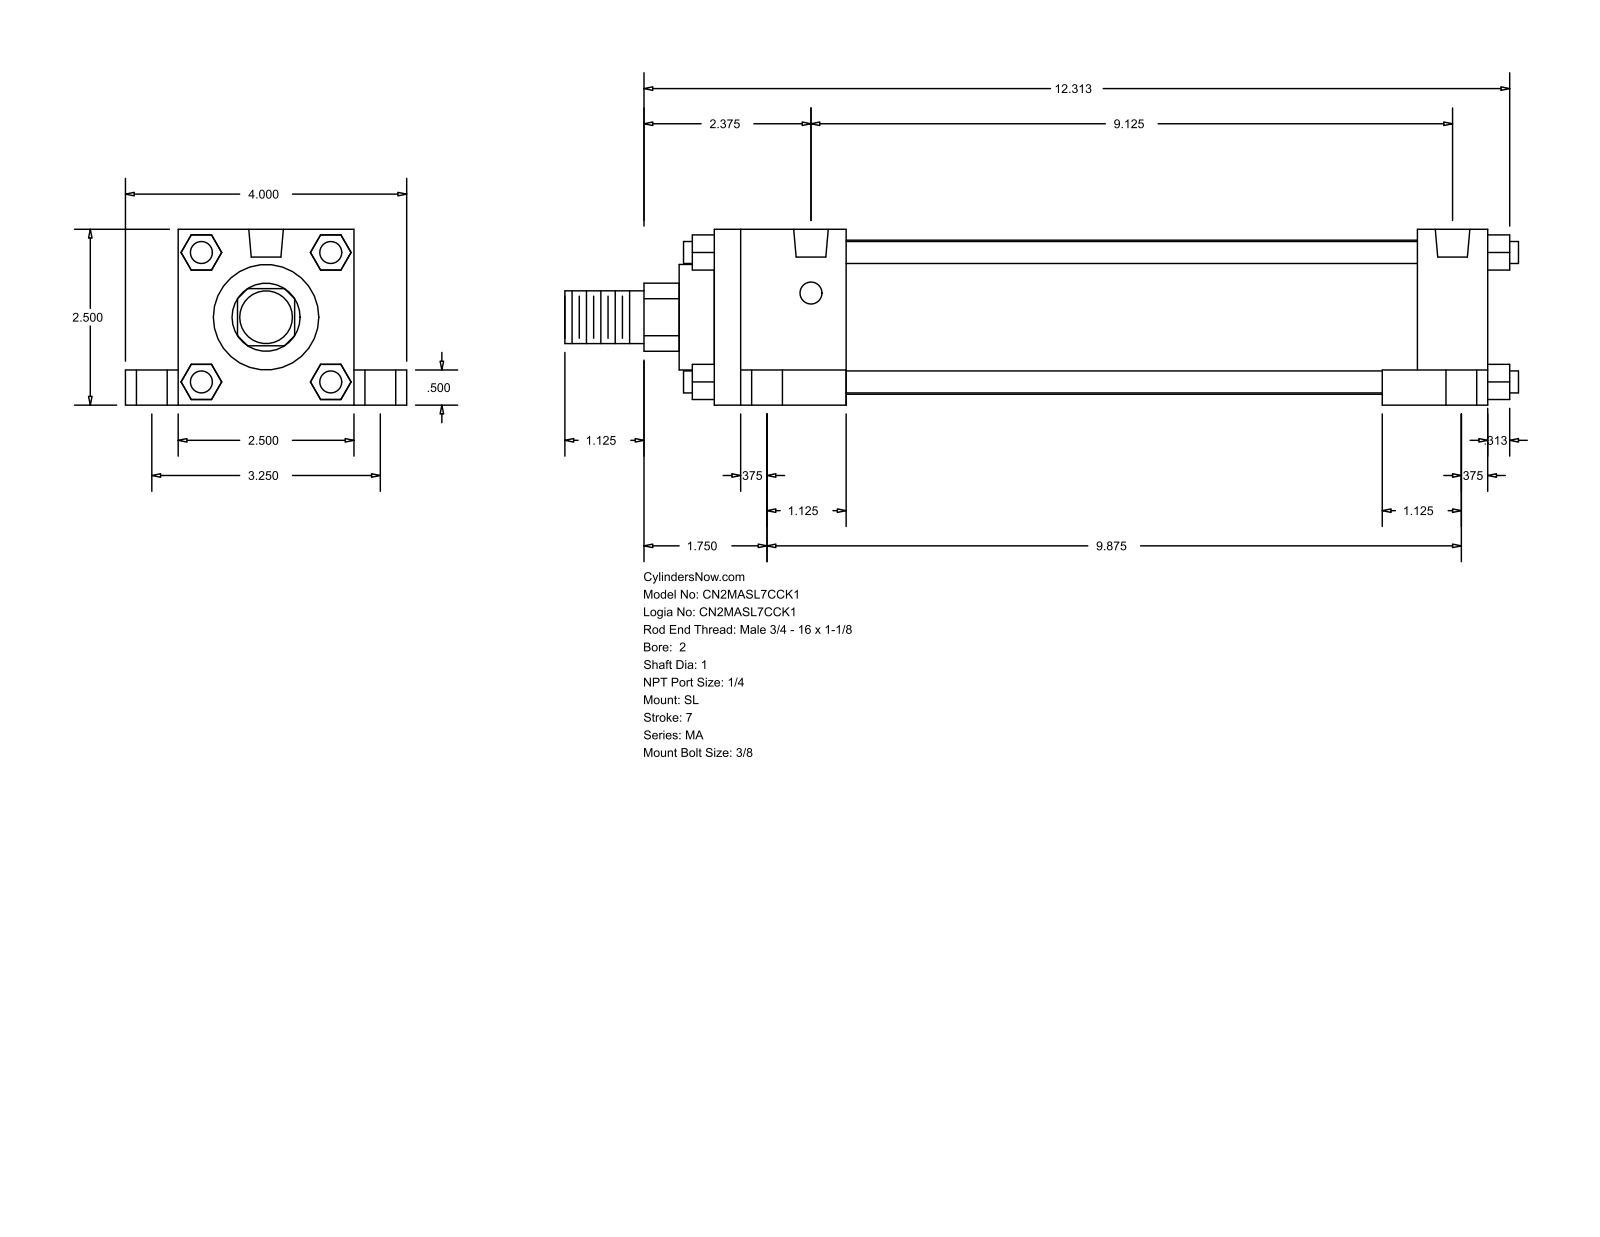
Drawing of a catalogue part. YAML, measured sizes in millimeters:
part_name: "MA_SL__0200_1"
step_written_by: "GSSL Pune (CONFIG_CONTROL_DESIGN)"
units: millimeters
bodies: {solids: 0, faces: 148, planar: 112, cylindrical: 36, other: 0}
overall_size: [344.49, 101.6, 63.5]
round_holes:
  - {diameter: 7.94, count: 4}
  - {diameter: 11.11, count: 4}
  - {diameter: 17.46, count: 4}
  - {diameter: 12.49, count: 2}
round_bosses_or_shafts:
  - {diameter: 7.94, count: 4}
  - {diameter: 55.63, count: 1}
  - {diameter: 38.1, count: 1}
  - {diameter: 25.4, count: 1}
  - {diameter: 19.05, count: 1}
partial_cylinders:
  - {radius: 12.29, count: 1}
face_to_face_distances: [63.5, 12.7, 279.4, 19.05, 82.55, 25.4, 50.8, 47.63, 231.77, 254]
hole_center_spacings: [41.39, 44.22, 82.54, 231.77, 238.54, 250.82, 251.07, 264.05]
